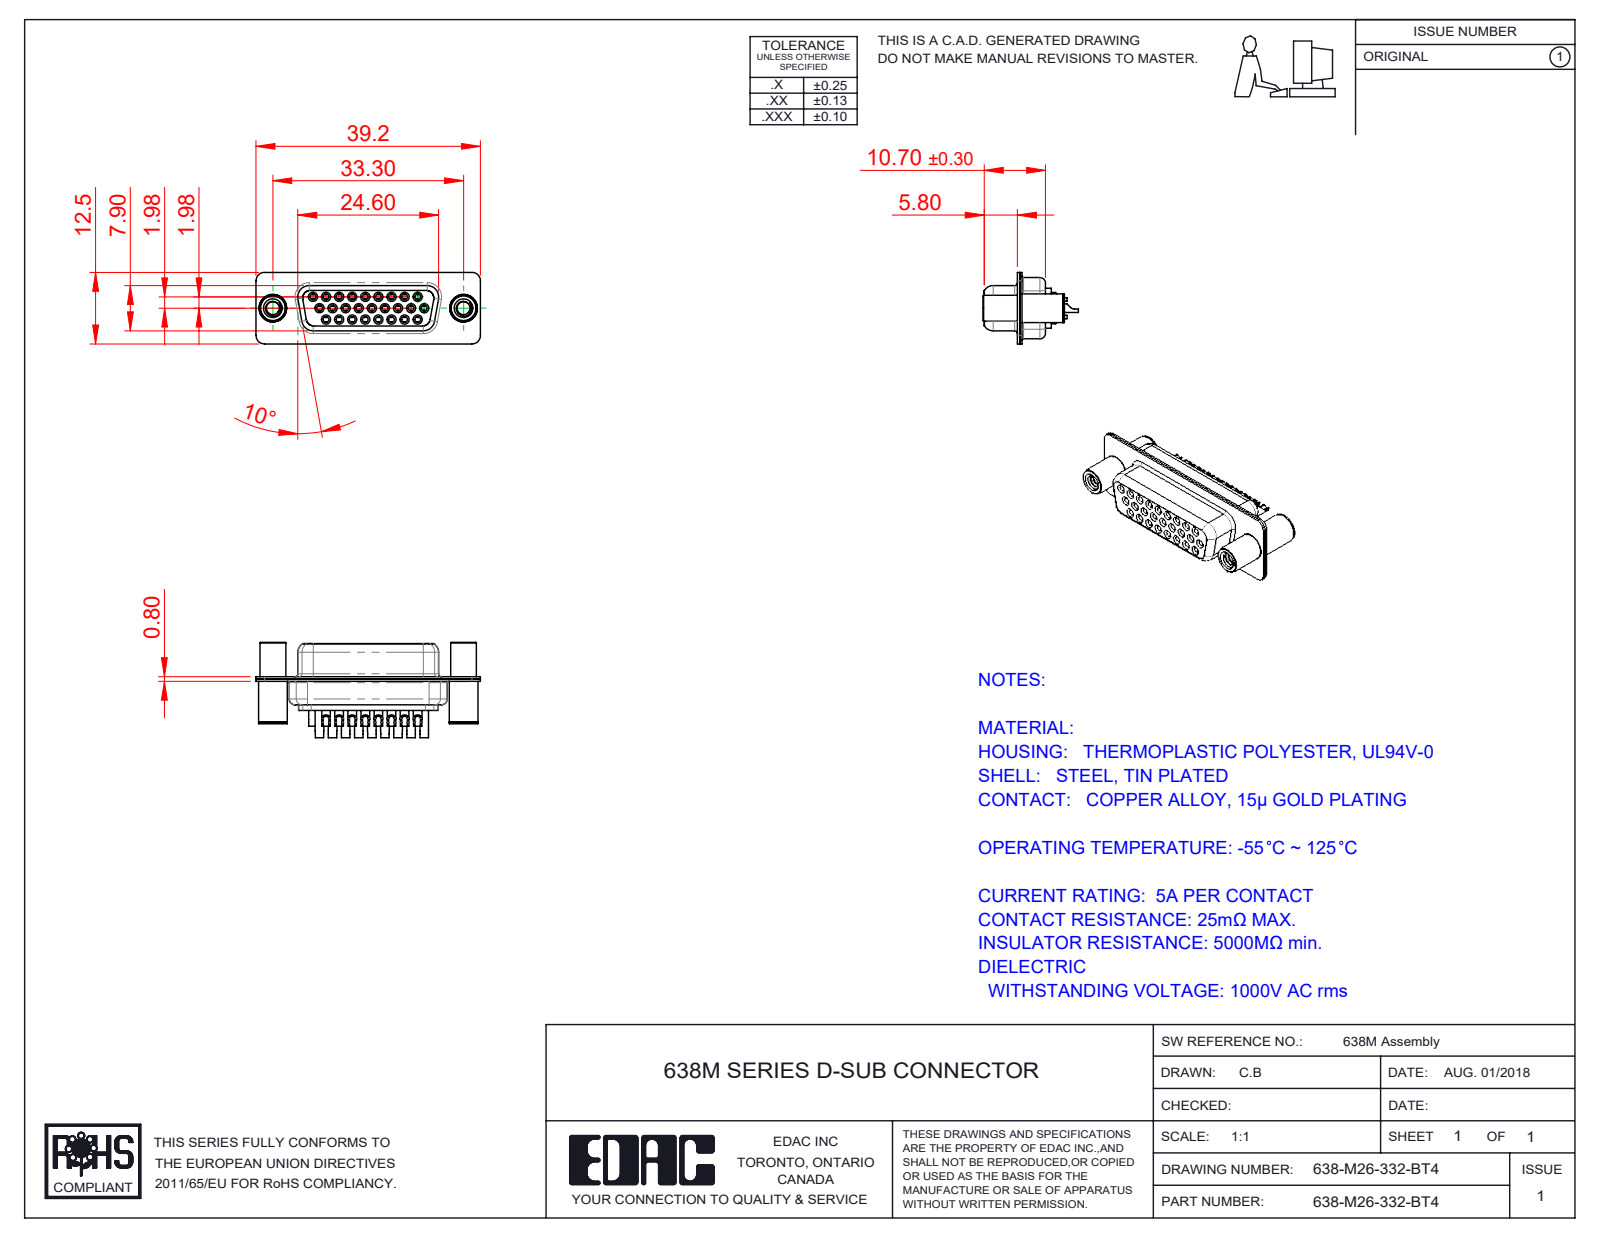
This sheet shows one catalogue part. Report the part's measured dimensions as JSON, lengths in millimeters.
{"part_name": "638M Housing_26 Contacts; 638M Contact Row 2_32; 638M 4-40 Threaded Standoff and Board Spacer; 638M Contact Row 1_32 (+4 more)", "step_written_by": "SolidWorks 2020 (CONFIG_CONTROL_DESIGN)", "units": "millimeters", "bodies": {"solids": 31, "faces": 1795, "planar": 515, "cylindrical": 735, "other": 545}, "overall_size": [39.2, 16.65, 12.5], "volume_mm3": 2679, "surface_area_mm2": 8575, "round_holes": [[1, 27], [1.1, 26], [1.7, 26], [1.8, 26], [2, 26], [2.26, 2], [3.26, 2], [4, 2], [4.8, 2]], "round_bosses_or_shafts": [[2.2, 26], [1.6, 26], [1.5, 26], [5, 2], [4.9, 2], [4.5, 2]], "partial_cylinders_radius": [[1.5, 16], [2, 12], [1.35, 8], [1.6, 8], [1, 7], [0.25, 4], [0.5, 4], [0.6, 4]], "face_to_face_distances": [0.4, 1.4, 0.45, 8.45, 8.9, 1.8, 1, 6.2, 7.05, 1.85], "hole_center_spacings": [3.96, 2.28, 4.57, 6.05, 2.29, 8.24, 6.86, 6.04]}
